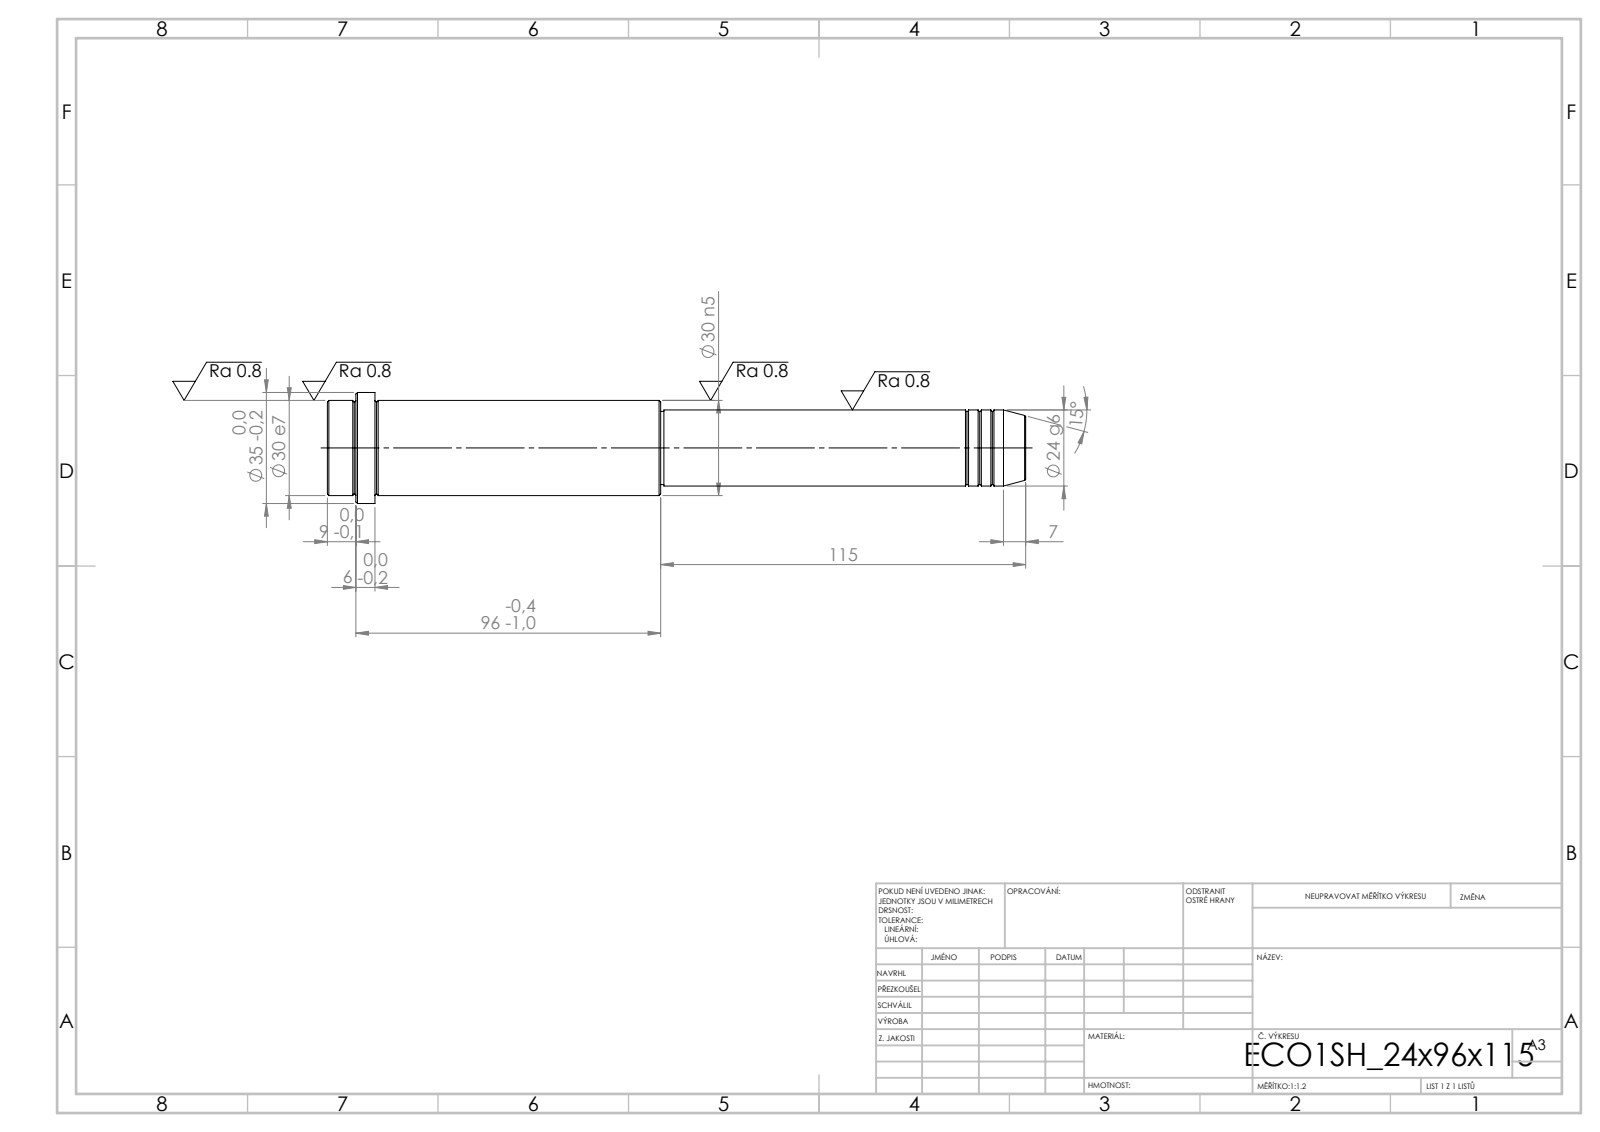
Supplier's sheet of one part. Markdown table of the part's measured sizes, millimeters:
| quantity | value |
| --- | --- |
| STEP written by | SolidWorks 2019 (CONFIG_CONTROL_DESIGN) |
| units | millimeters |
| bodies | 1 solid, 52 faces (6 planar, 16 cylindrical, 30 other) |
| overall size | 220 × 35 × 35 |
| volume | 127 071 mm³ |
| surface area | 20 627 mm² |
| round bosses / shafts (diameter × count) | 35 × 1, 30 × 1, 24 × 1, 23 × 1 |
| main face-to-face distances | 220, 205, 15, 115, 90, 105, 211, 96, 6, 9 |
